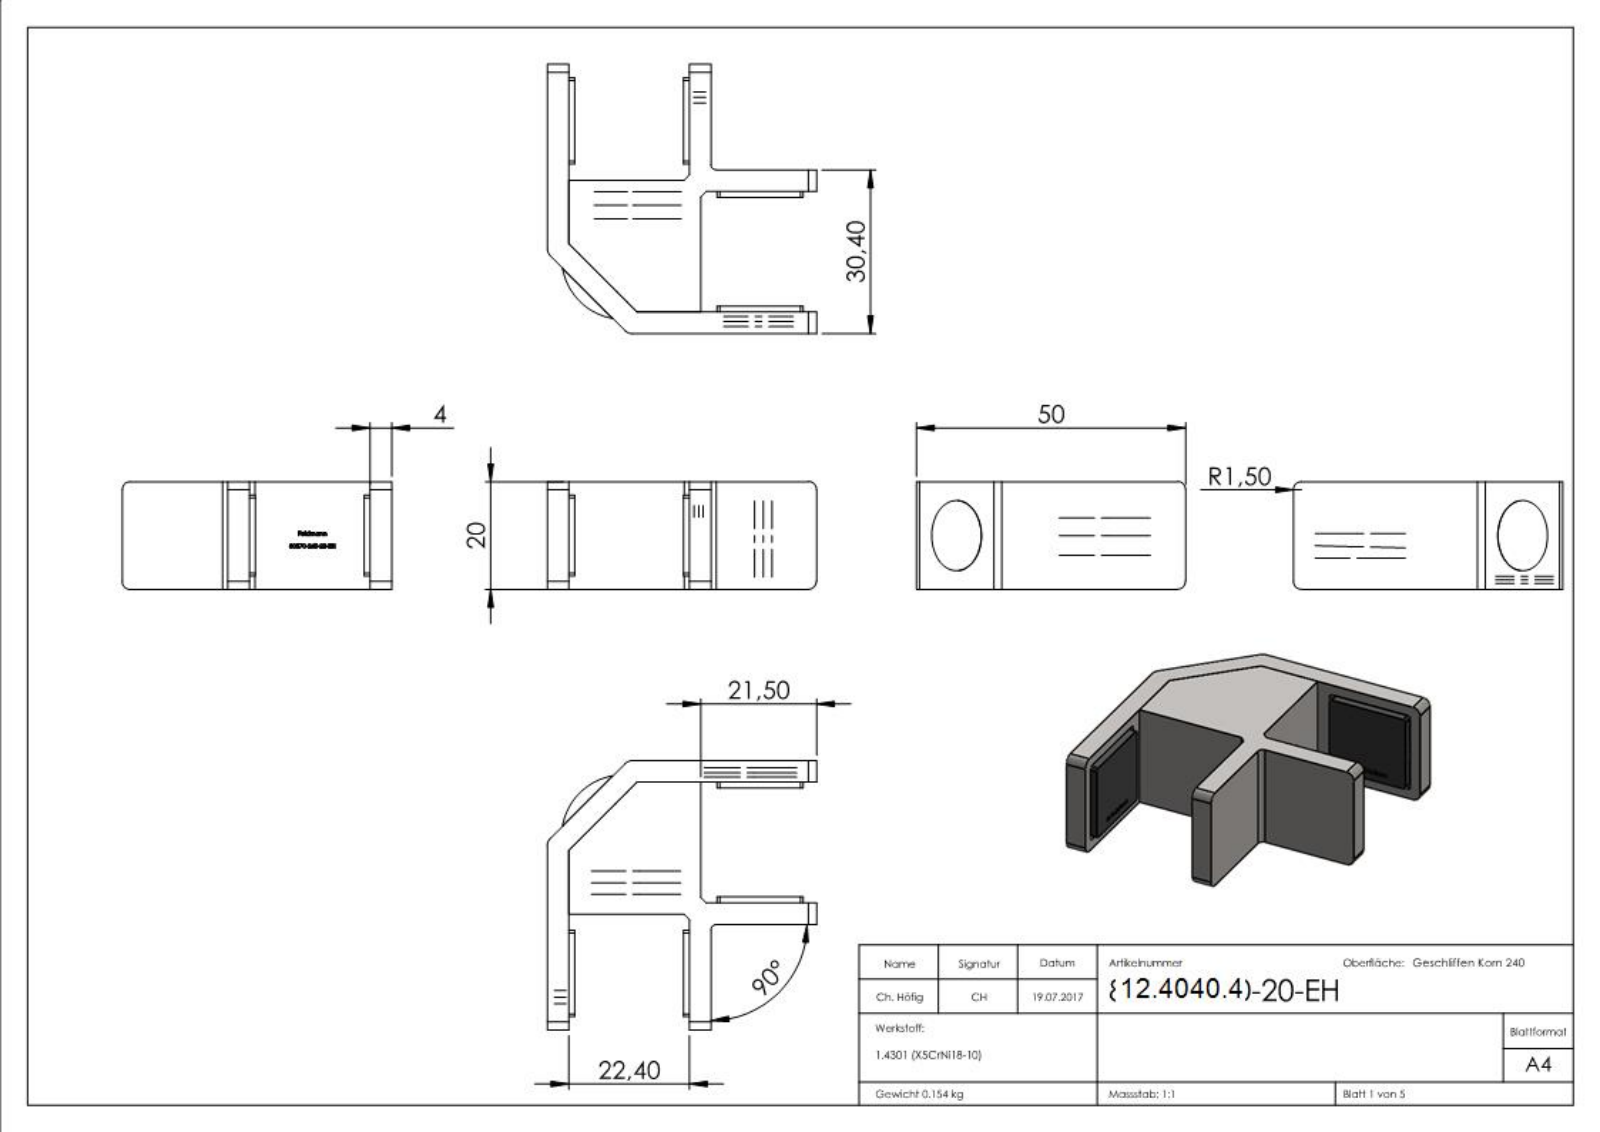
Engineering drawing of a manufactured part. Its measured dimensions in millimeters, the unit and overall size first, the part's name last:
Units: millimetres
Overall size (bounding box): 50 × 50 × 20
Round holes (diameter × count): ⌀2.7 ×2, ⌀1.8 ×1, ⌀5 ×1, ⌀7 ×1, ⌀12.5 ×1
Round bosses / shafts (diameter × count): ⌀11.57 ×1, ⌀6 ×1, ⌀4 ×1
Partial cylindrical surfaces — rounded edges, fillets, slot ends (radius × count): R0.2 ×56, R0.5 ×48, R1.5 ×4, R2 ×2, R1 ×1
Main face-to-face distances: 4, 1.6, 3.5, 0.5, 26.9, 26.4, 23.4, 5.1, 20, 22.9
Hole centre spacings: 8.2, 16.4
Volume: 21 448 mm³ · Surface area: 13 533 mm²
Bodies: 8 solids, 2925 faces (1602 planar, 209 cylindrical, 1114 other)
Part name (STEP PRODUCT): 80570-xxx-xx-EH Teil3; socket countersunk head screw_din; 80570-xxx-xx-EH Teil1; 80570-240-20-EH (+6 more)
STEP written by: SolidWorks 2018 (CONFIG_CONTROL_DESIGN)
